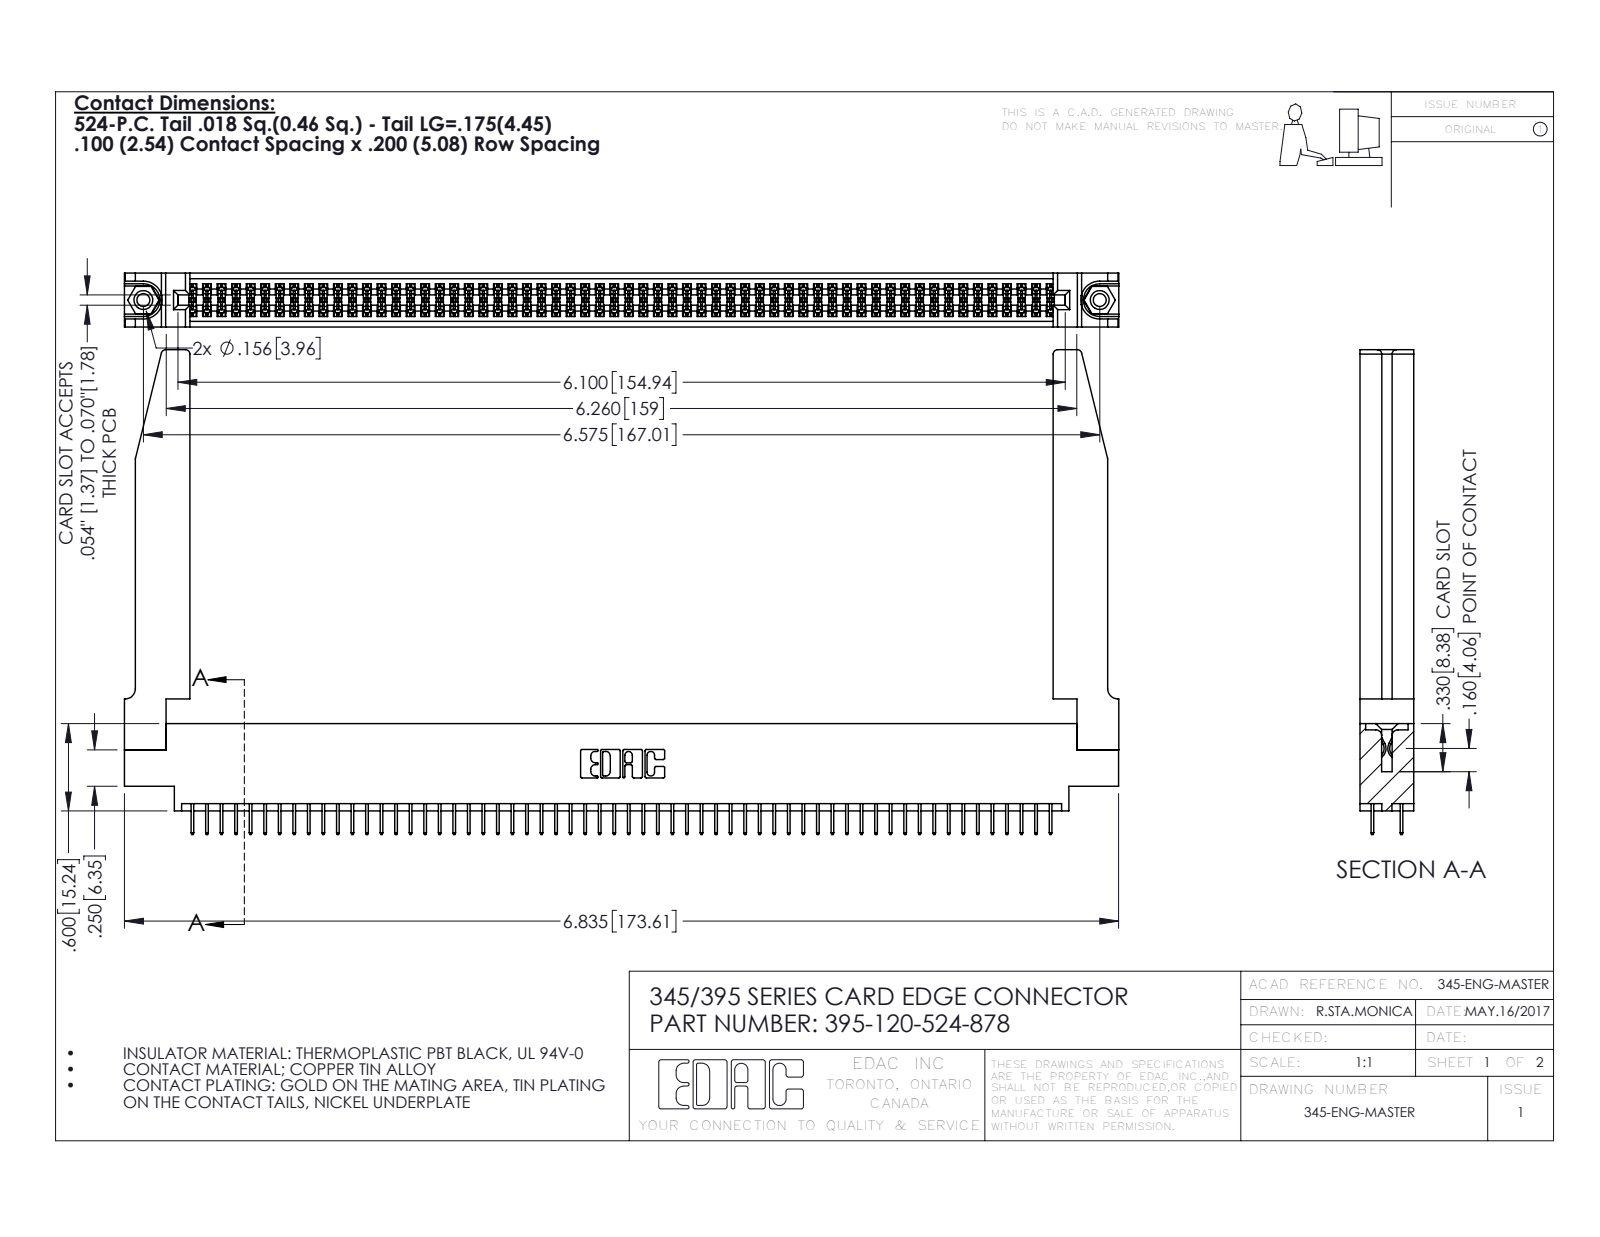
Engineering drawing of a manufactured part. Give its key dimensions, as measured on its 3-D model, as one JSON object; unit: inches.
{"part_name": "395-120-524-878; 345 Part_0.170 Offset - 0.156 Dia-TH; 345-250-001_345-250-001-102; 345-292-001_345-293-124 (+1 more)", "step_written_by": "SolidWorks 2016 (CONFIG_CONTROL_DESIGN)", "units": "inches", "bodies": {"solids": 125, "faces": 6844, "planar": 4906, "cylindrical": 1886, "other": 52}, "overall_size": [6.836, 3.332, 0.37], "volume_in3": 1.496, "surface_area_in2": 48.97, "round_holes": [[0.089, 2], [0.125, 2], [0.156, 2], [0.064, 1]], "round_bosses_or_shafts": [[0.155, 2]], "partial_cylinders_radius": [[0.006, 180], [0.01, 22], [0.03, 8], [0.007, 6], [0.031, 6], [0.026, 3], [0.014, 2], [0.019, 2]], "face_to_face_distances": [0.072, 0.37, 0.298, 0.2, 0.098, 0.272, 0.025, 0.225, 0.072, 0.175], "hole_center_spacings": [0.27, 6.339, 6.575]}
